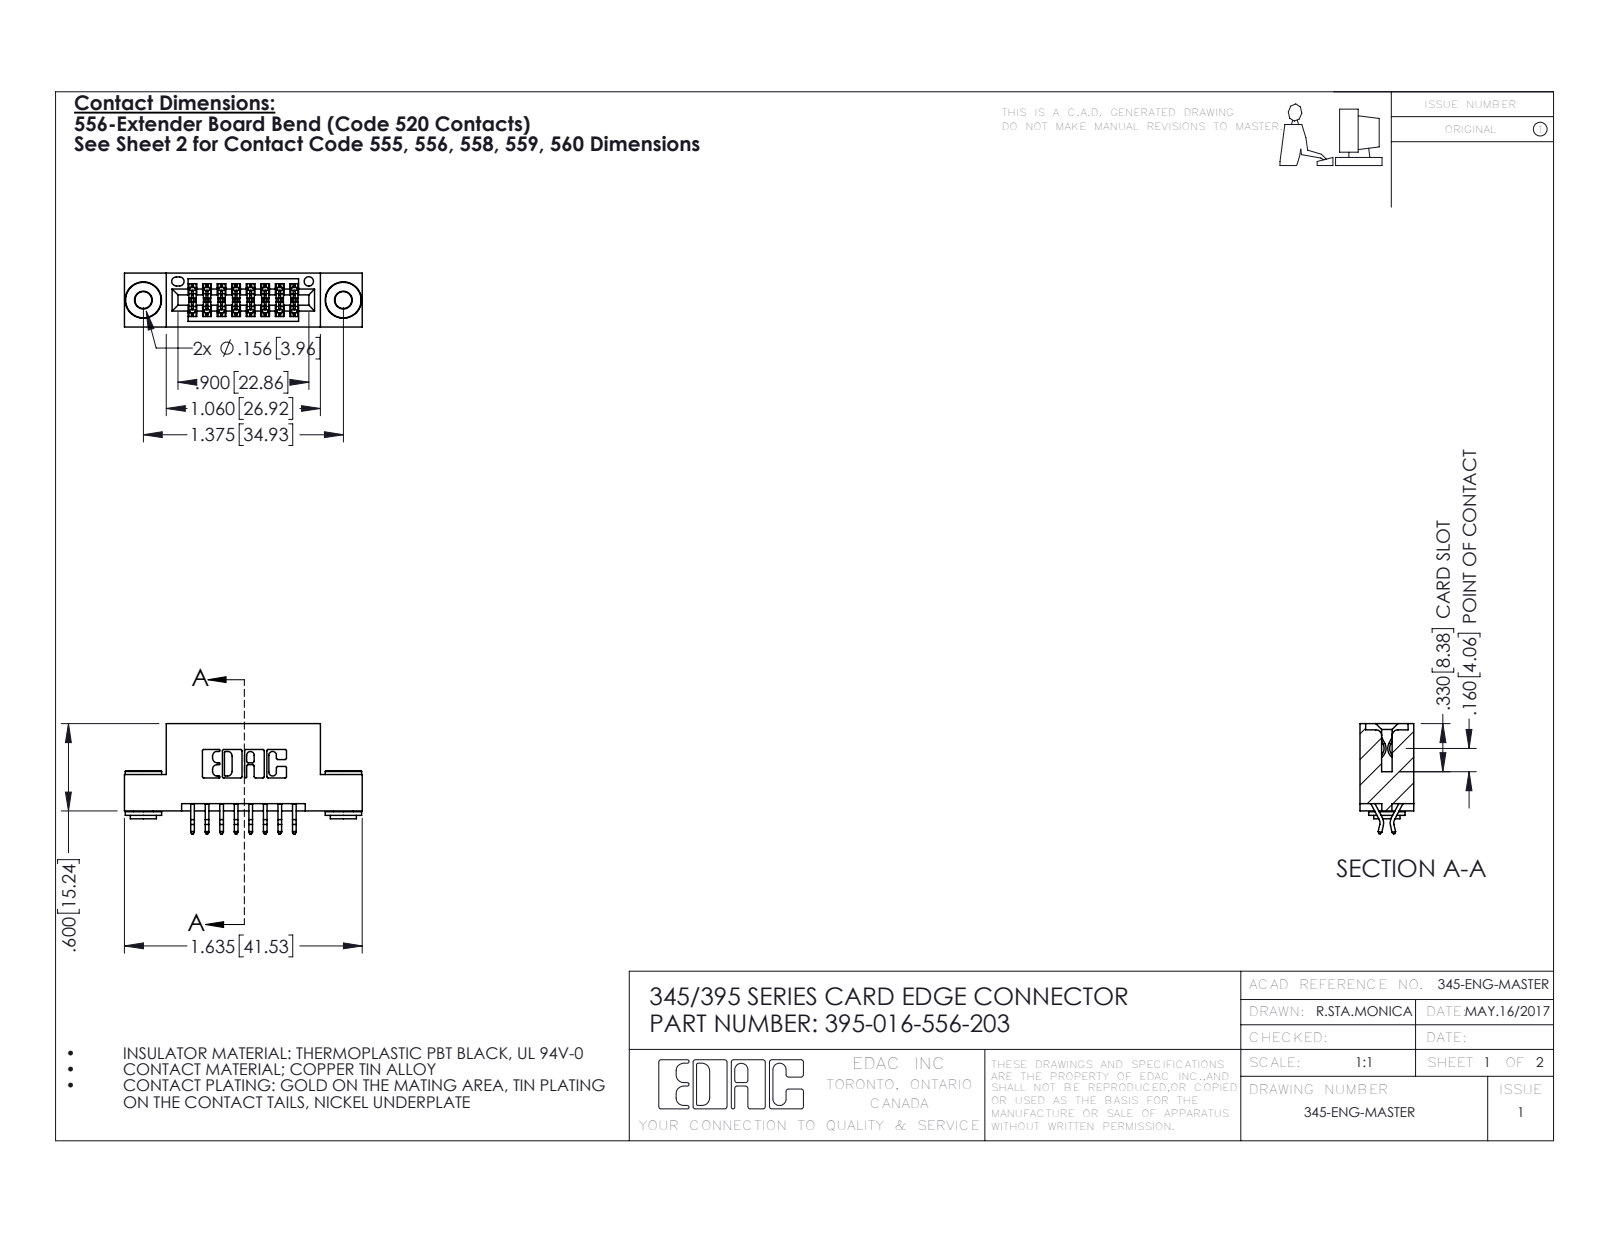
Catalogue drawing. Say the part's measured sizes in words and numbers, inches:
The part is named "345-292-001_556 Tail; 345 Part_Flush Mounting Lugs - 0.156 Dia-TH; 345-250-002_345-250-002-102; 395-016-556-203". Its 3-D file was written by "SolidWorks 2016 (CONFIG_CONTROL_DESIGN)". It is 19 solids with 1060 faces: 682 planar, 370 cylindrical and 8 other. Overall it measures 1.635 by 0.757 by 0.37 inches. Its volume is 0.228 cubic inches and its surface area 7.838 square inches. Round holes: 2 of diameter 0.116, 2 of diameter 0.156, 1 of diameter 0.064. Round bosses or shafts: 2 of diameter 0.25, 2 of diameter 0.18, 2 of diameter 0.136. Partial cylindrical surfaces (rounded edges, fillets, slot ends): 24 of radius 0.006, 22 of radius 0.01, 6 of radius 0.007, 6 of radius 0.031, 3 of radius 0.026, 2 of radius 0.01, 2 of radius 0.014, 2 of radius 0.019. The main face-to-face distances are 0.2, 0.072, 0.298, 0.37, 0.1, 0.3, 0.025, 0.225, 0.098, 0.272. The hole center spacings are 0.27, 1.144, 1.375.
